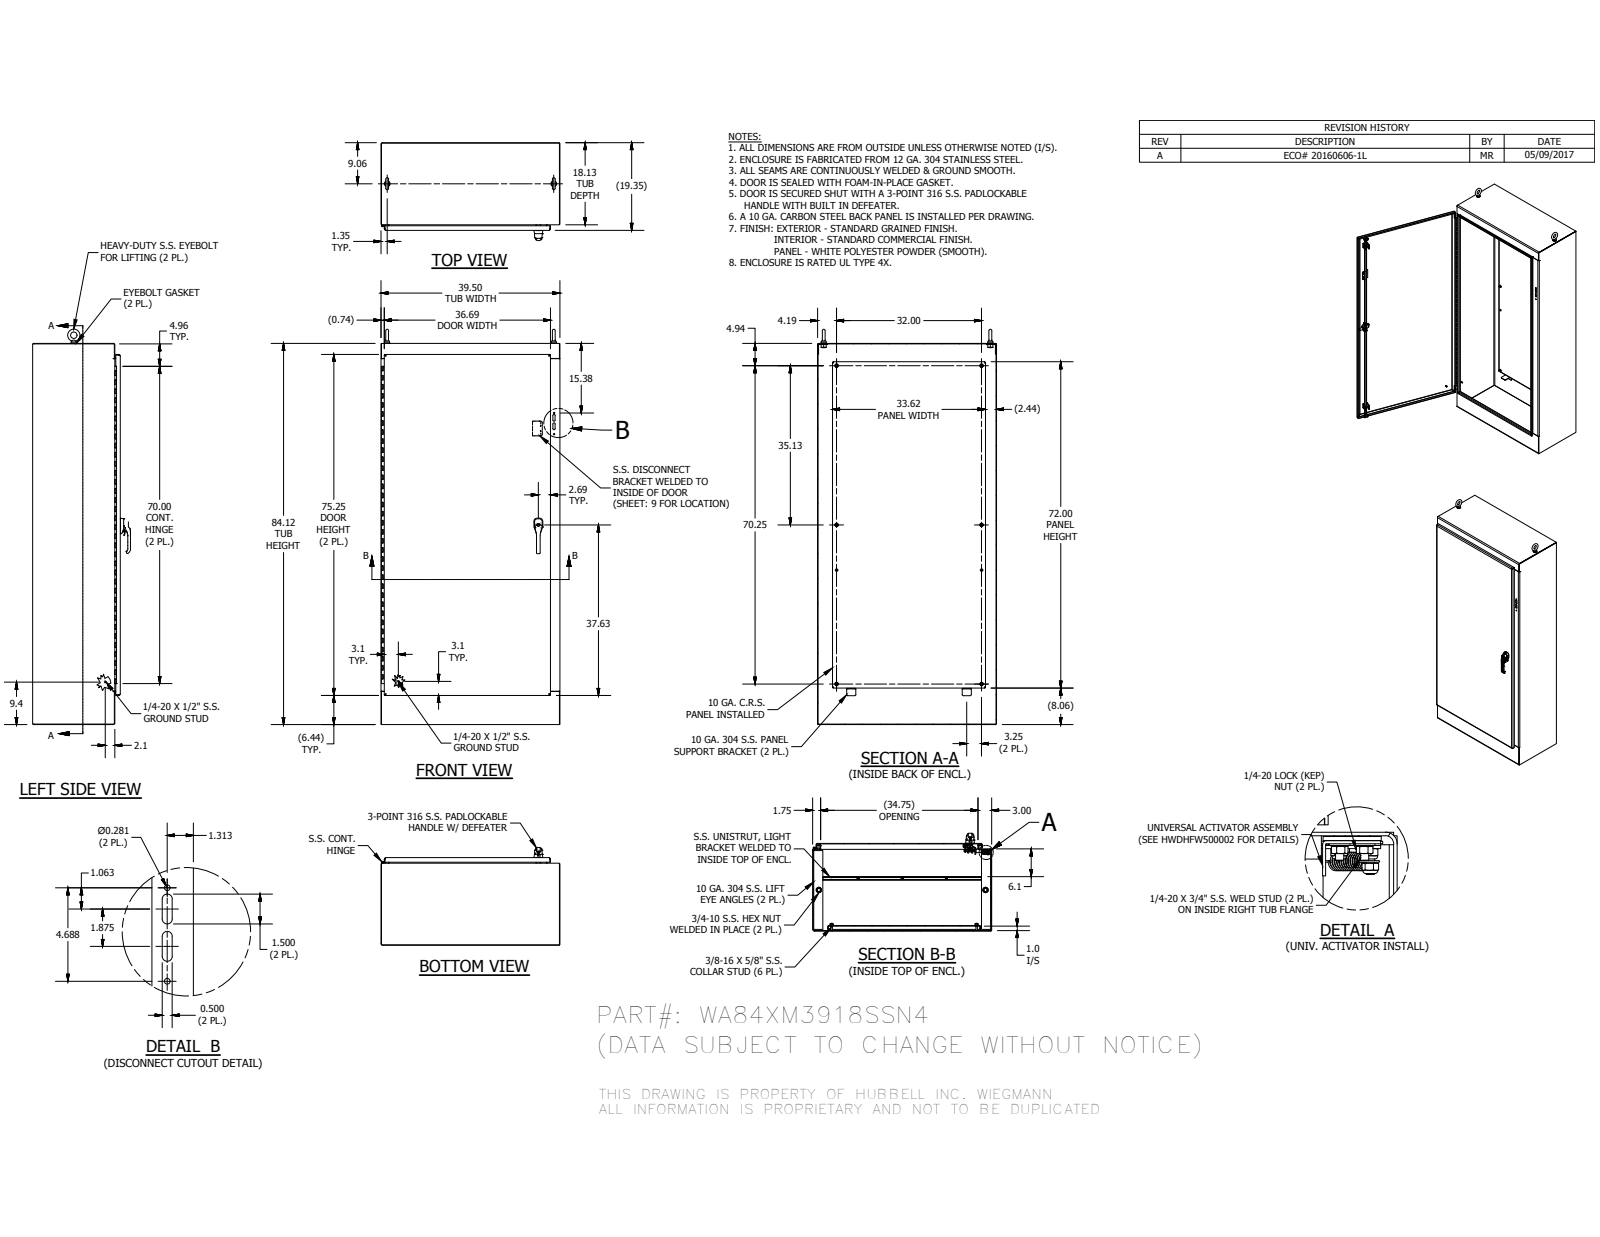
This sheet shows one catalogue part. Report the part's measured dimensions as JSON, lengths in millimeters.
{"part_name": "WA84XM3918SSN4BLS; WAXM3918SSN4TOP; WAXM3918SSN4BTM; FUN00129_WAXM39SSN4 (+8 more)", "step_written_by": "Autodesk Inventor 2016 (AUTOMOTIVE_DESIGN)", "units": "millimeters", "bodies": {"solids": 127, "faces": 4841, "planar": 2251, "cylindrical": 1548, "other": 1042}, "overall_size": [2216.09, 1003.3, 548.55], "volume_mm3": 27750000, "surface_area_mm2": 19700000, "round_holes": [[3.55, 24], [9.52, 10], [6.35, 9], [6.65, 8], [14.29, 8], [3.96, 6], [7.8, 6], [4.76, 5], [3.45, 4], [4.17, 4], [5.1, 4], [7.37, 4]], "round_bosses_or_shafts": [[15.88, 10], [8.38, 9], [14.29, 6], [13.54, 4], [8.56, 4], [6.35, 4], [6.02, 4], [6, 3]], "partial_cylinders_radius": [[0.5, 187], [0.3, 109], [0.51, 48], [6.35, 25], [0.47, 21], [1.59, 20], [3.17, 18], [0.64, 16]], "face_to_face_distances": [2.64, 488.79, 1000.66, 486.15, 491.43, 3.41, 25.4, 463.39, 457.34, 31.45], "hole_center_spacings": [0.45, 395.11, 0.6, 1680.23, 9.65, 19.31, 197.56, 790.22]}
